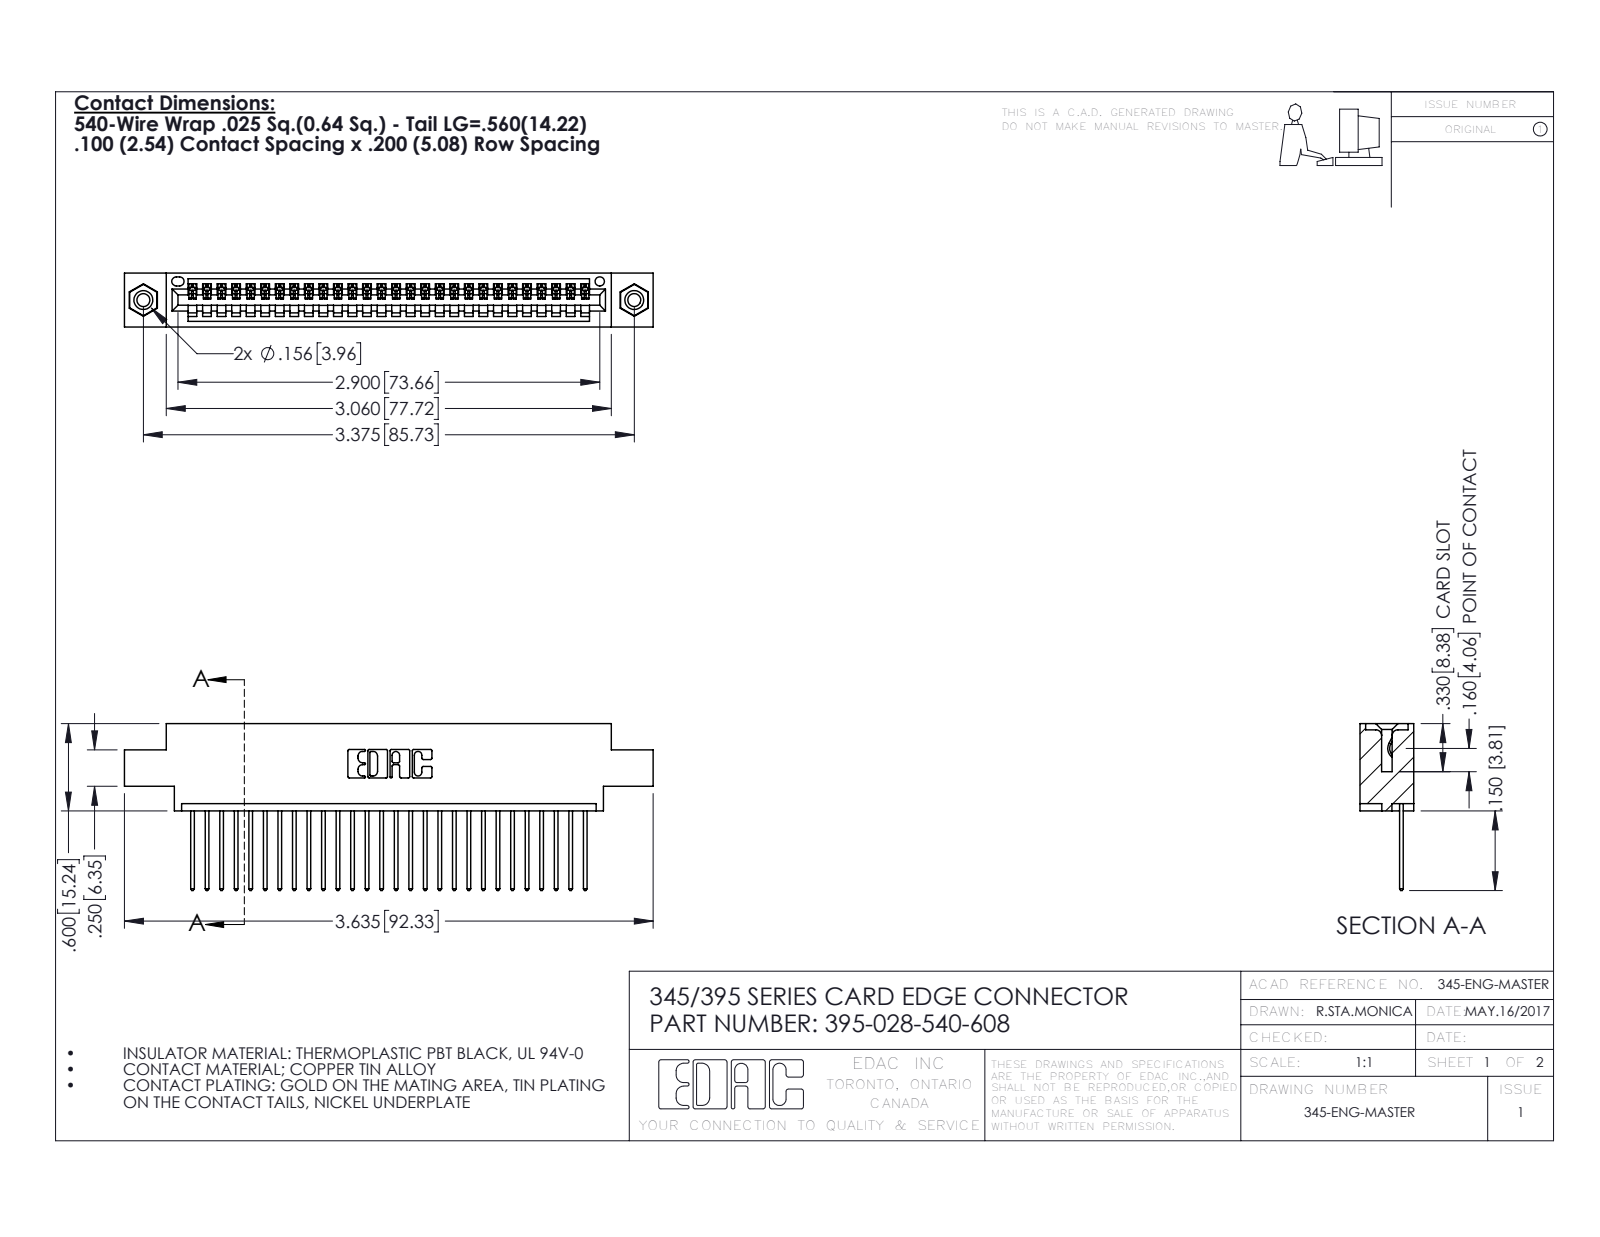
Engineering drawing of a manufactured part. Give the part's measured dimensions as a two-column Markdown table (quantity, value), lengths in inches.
| quantity | value |
| --- | --- |
| part name | 345-250-001_345-250-003-102; 345-292-001_345-293-140; 395-028-540-608; 345 Part_0.170 Offset - 0.156 Dia-TI |
| STEP written by | SolidWorks 2016 (CONFIG_CONTROL_DESIGN) |
| units | inches |
| bodies | 31 solids, 1814 faces (1236 planar, 562 cylindrical, 16 other) |
| overall size | 3.635 × 1.147 × 0.37 |
| volume | 0.523 in³ |
| surface area | 18.01 in² |
| round holes (diameter × count) | 0.089 × 2, 0.125 × 2, 0.156 × 2, 0.064 × 1 |
| round bosses / shafts (diameter × count) | 0.155 × 2 |
| partial cylindrical surfaces (radius × count) | 0.006 × 56, 0.01 × 56, 0.01 × 22, 0.007 × 6, 0.031 × 6, 0.026 × 3, 0.031 × 2, 0.04 × 2 |
| main face-to-face distances | 0.072, 0.298, 0.37, 0.2, 0.098, 0.272, 0.025, 0.225, 0.175, 0.149 |
| hole center spacings | 0.27, 3.14, 3.375 |
